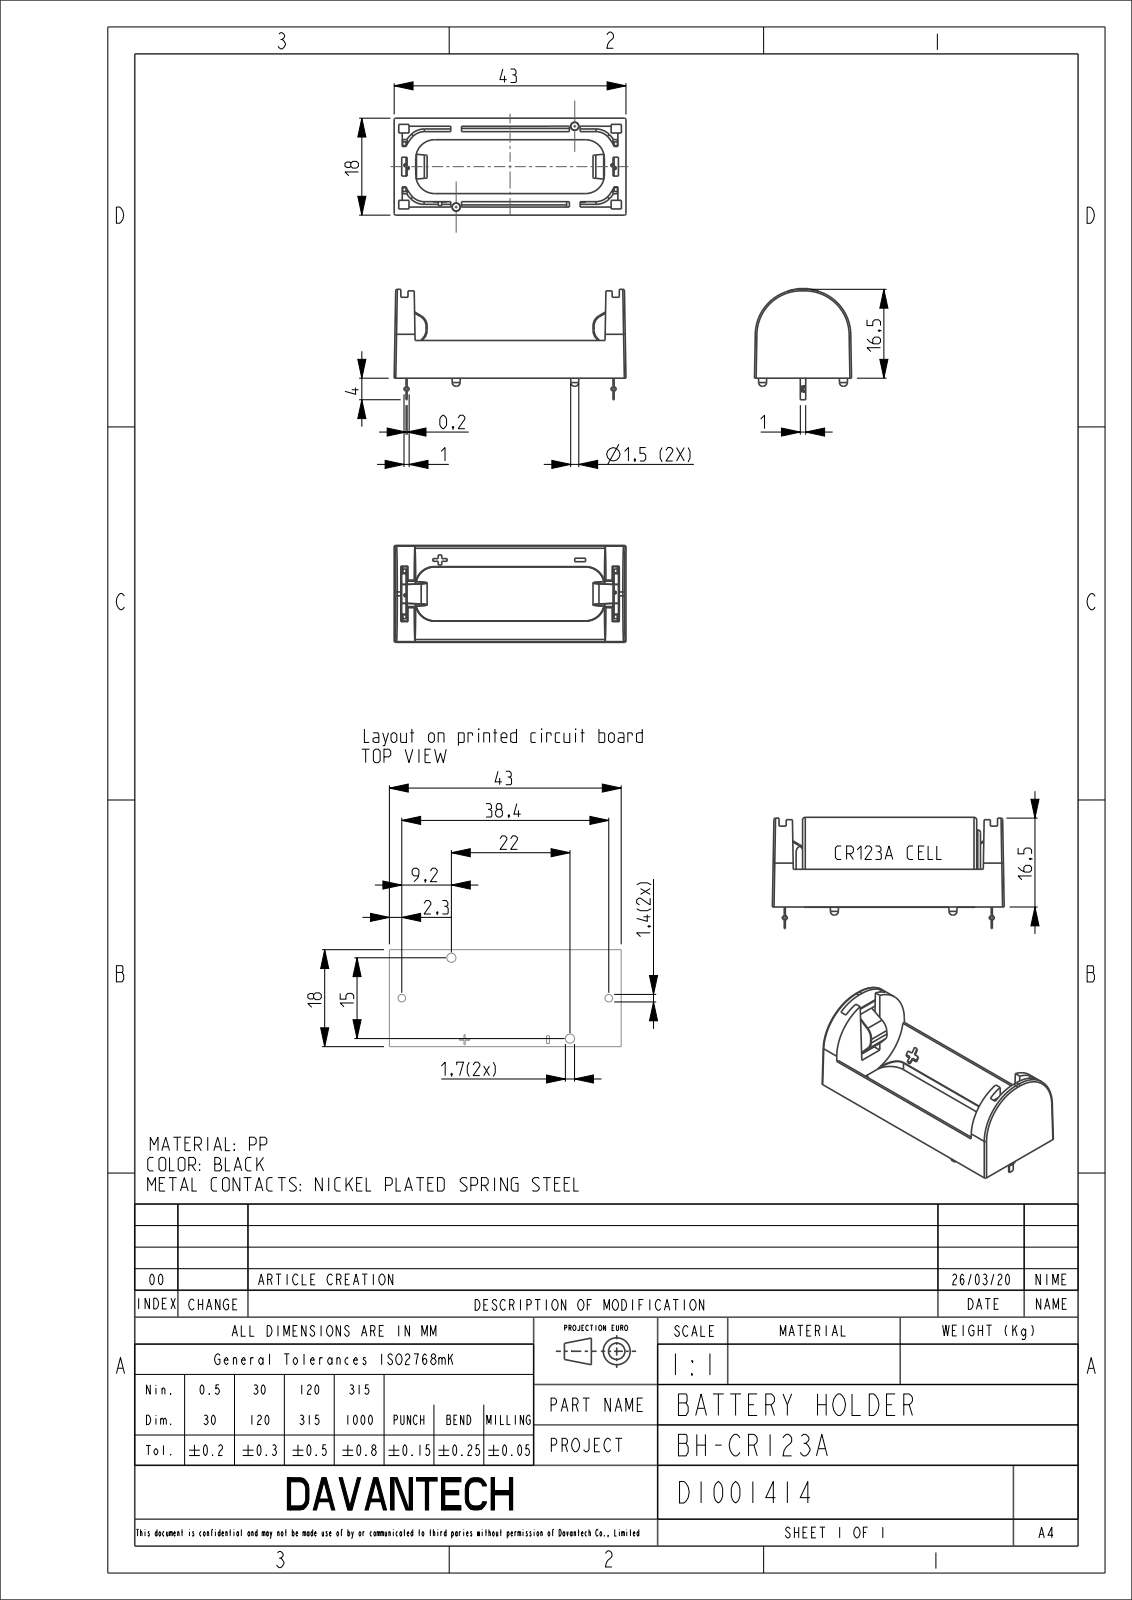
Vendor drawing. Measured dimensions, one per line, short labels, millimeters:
name: D1001415; D1001416; D1001414_ASM
written by: CREO PARAMETRIC BY PTC INC, 2020154 (CONFIG_CONTROL_DESIGN)
unit: mm
bodies: 3 solids, 337 faces (247 planar, 62 cylindrical, 28 other)
size: 43 × 20.5 × 18
volume: 2 272 mm³; area: 4 347 mm²
rounds: 22× R0.2, 10× R0.3, 4× R2, 4× R2.2, 4× R3, 4× R3.5, 2× R0.1, 2× R0.2
face distances: 39, 39.2, 14, 0.35, 1.35, 38.4, 1.25, 15.35, 1, 14.35
